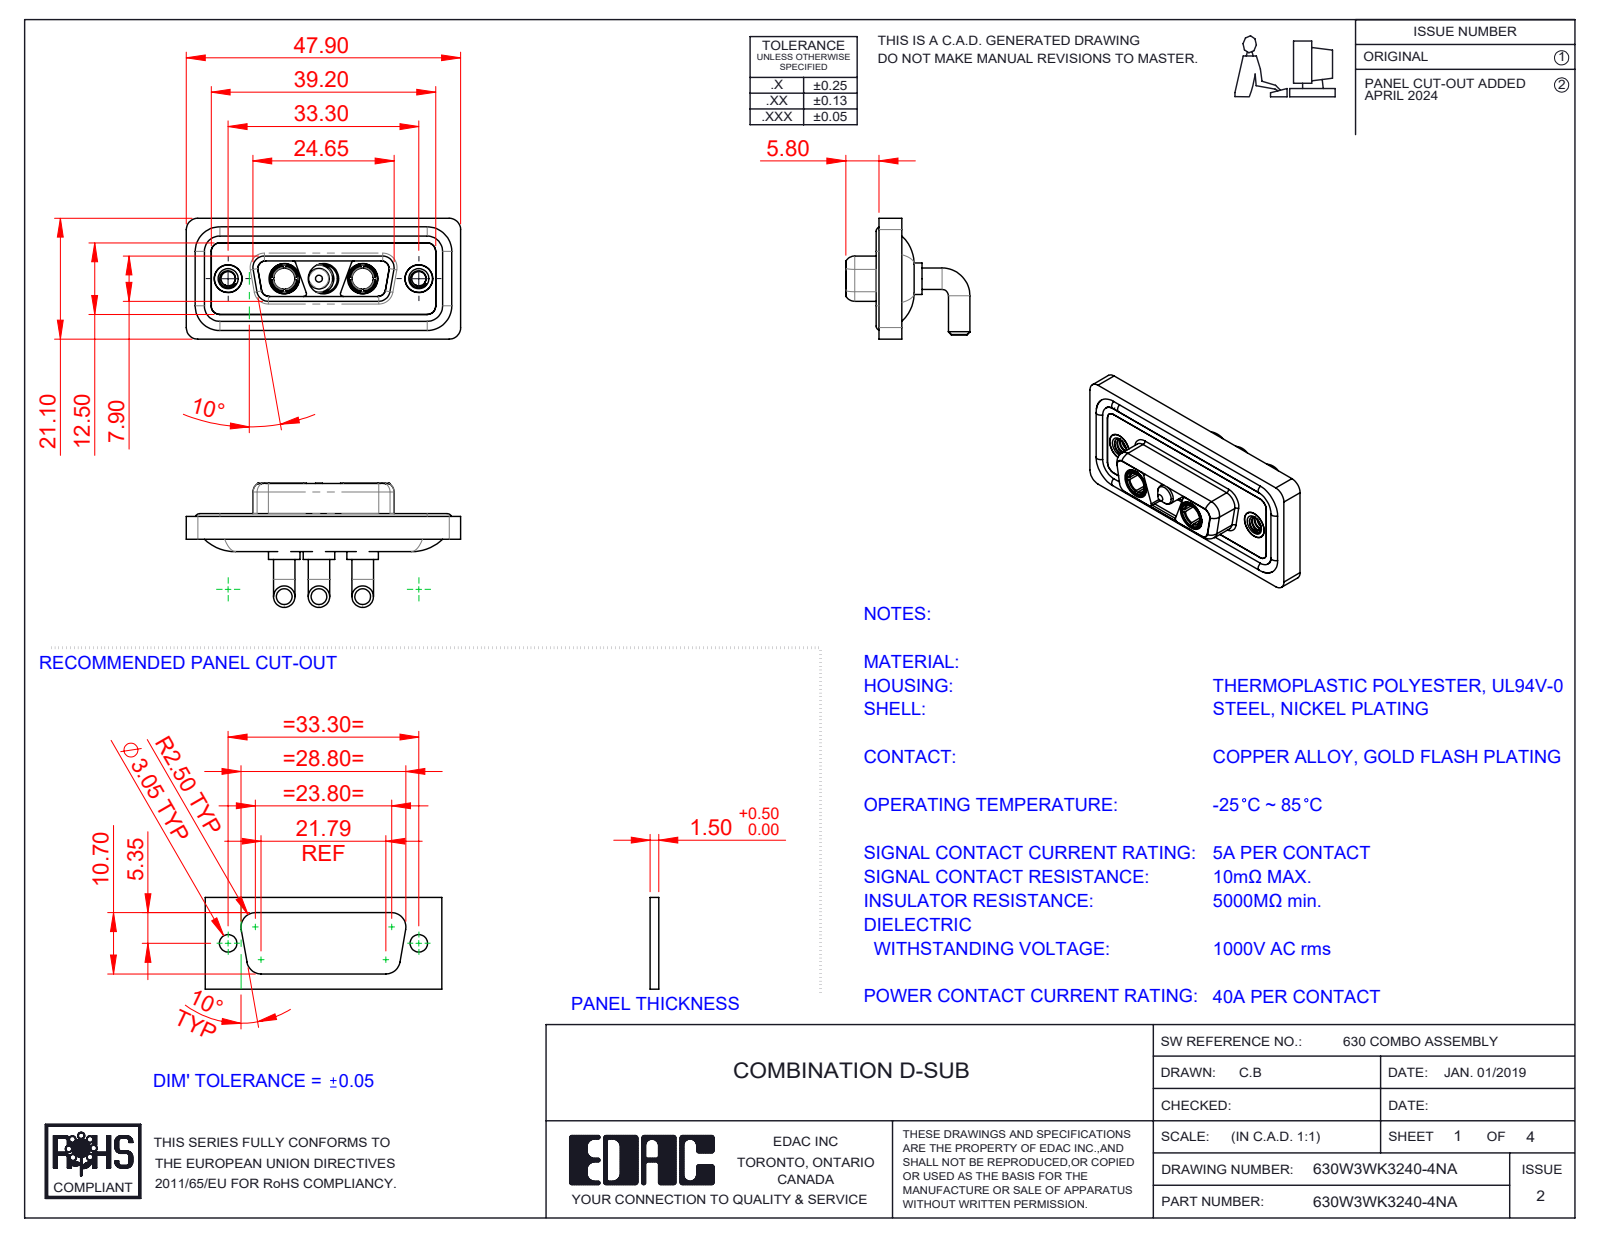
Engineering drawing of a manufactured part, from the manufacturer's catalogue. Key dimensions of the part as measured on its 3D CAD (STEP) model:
Part name (STEP PRODUCT): 630Combo Shell Rear_15 Contacts; 630Combo Housing_3WK3; Power Pin_40A RA; Power Socket_40A RA (+4 more)
STEP written by: SolidWorks 2023 (CONFIG_CONTROL_DESIGN)
Units: millimetres
Bodies: 13 solids, 589 faces (178 planar, 262 cylindrical, 149 other)
Overall size (bounding box): 47.9 × 21.68 × 21.1
Volume: 6 243 mm³ · Surface area: 9 873 mm²
Round holes (diameter × count): ⌀4.85 ×5, ⌀5.3 ×3, ⌀2.5 ×2, ⌀3.7 ×2, ⌀4 ×2, ⌀4.05 ×2, ⌀5 ×2
Round bosses / shafts (diameter × count): ⌀3.75 ×6, ⌀1.6 ×4, ⌀5.5 ×3, ⌀5.2 ×3, ⌀4.75 ×3, ⌀4.96 ×2, ⌀4.95 ×2, ⌀4.8 ×2
Partial cylindrical surfaces — rounded edges, fillets, slot ends (radius × count): R2 ×20, R1.5 ×18, R1.35 ×12, R0.5 ×8, R1.6 ×8, R0.25 ×4, R0.6 ×4, R0.65 ×4
Main face-to-face distances: 0.4, 1.8, 1.1, 1.6, 2.9, 2.5, 3.1, 3.7, 4.1, 1.5
Hole centre spacings: 6.85, 9.8, 16.65, 23.5, 13.7, 33.3
